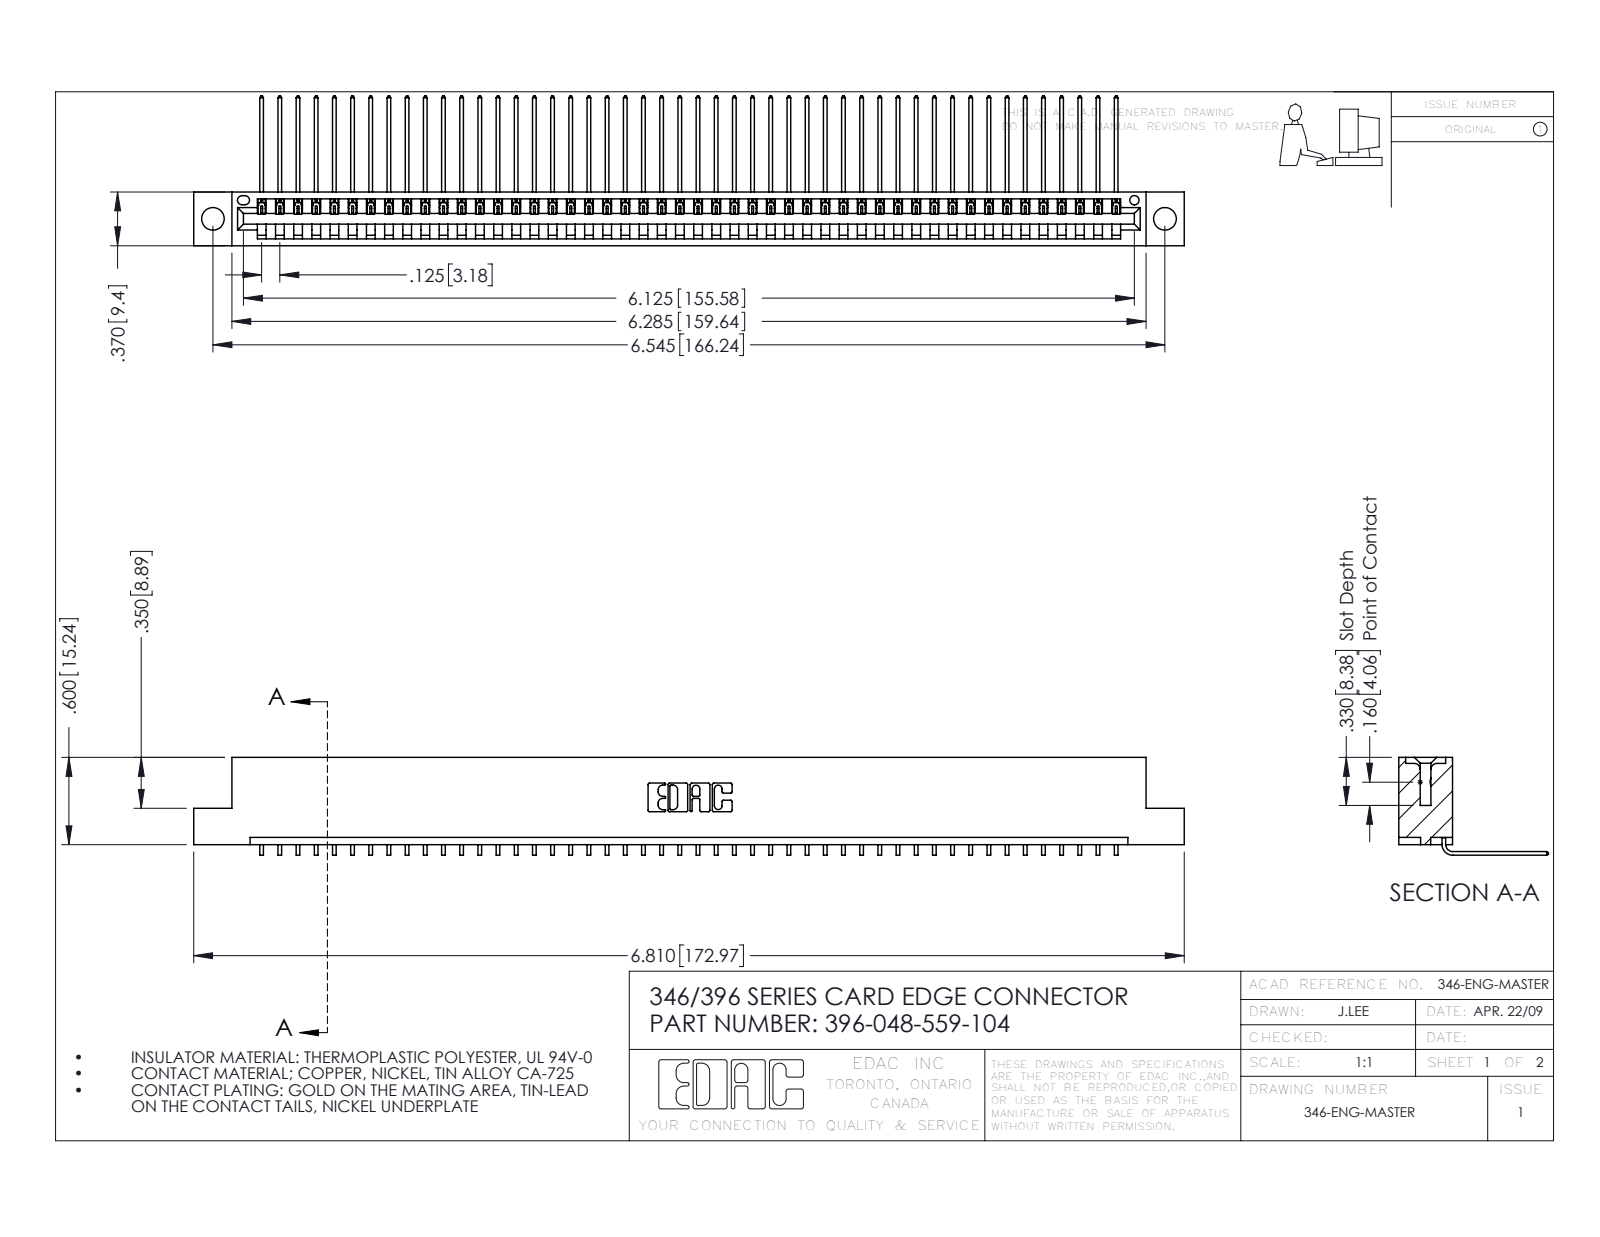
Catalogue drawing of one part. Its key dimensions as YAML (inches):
part_name: "396-048-559-104; 346 Part_Flush Mounting Lugs - 0.156 Dia-TH; 345-292-001_558 559 Tail - 1"
step_written_by: "SolidWorks 2016 (CONFIG_CONTROL_DESIGN)"
units: inches
bodies: {solids: 49, faces: 3002, planar: 2092, cylindrical: 910, other: 0}
overall_size: [6.81, 1.03, 0.673]
volume: 1.017
surface_area: 33.57
round_holes:
  - {diameter: 0.156, count: 2}
  - {diameter: 0.064, count: 1}
partial_cylinders:
  - {radius: 0.006, count: 96}
  - {radius: 0.01, count: 22}
  - {radius: 0.007, count: 6}
  - {radius: 0.031, count: 6}
  - {radius: 0.026, count: 3}
  - {radius: 0.031, count: 2}
  - {radius: 0.04, count: 2}
  - {radius: 0.014, count: 1}
face_to_face_distances: [0.048, 0.322, 0.37, 0.025, 0.25, 0.072, 0.298, 0.148, 0.222, 0.1]
hole_center_spacings: [0.246, 6.336, 6.545]
